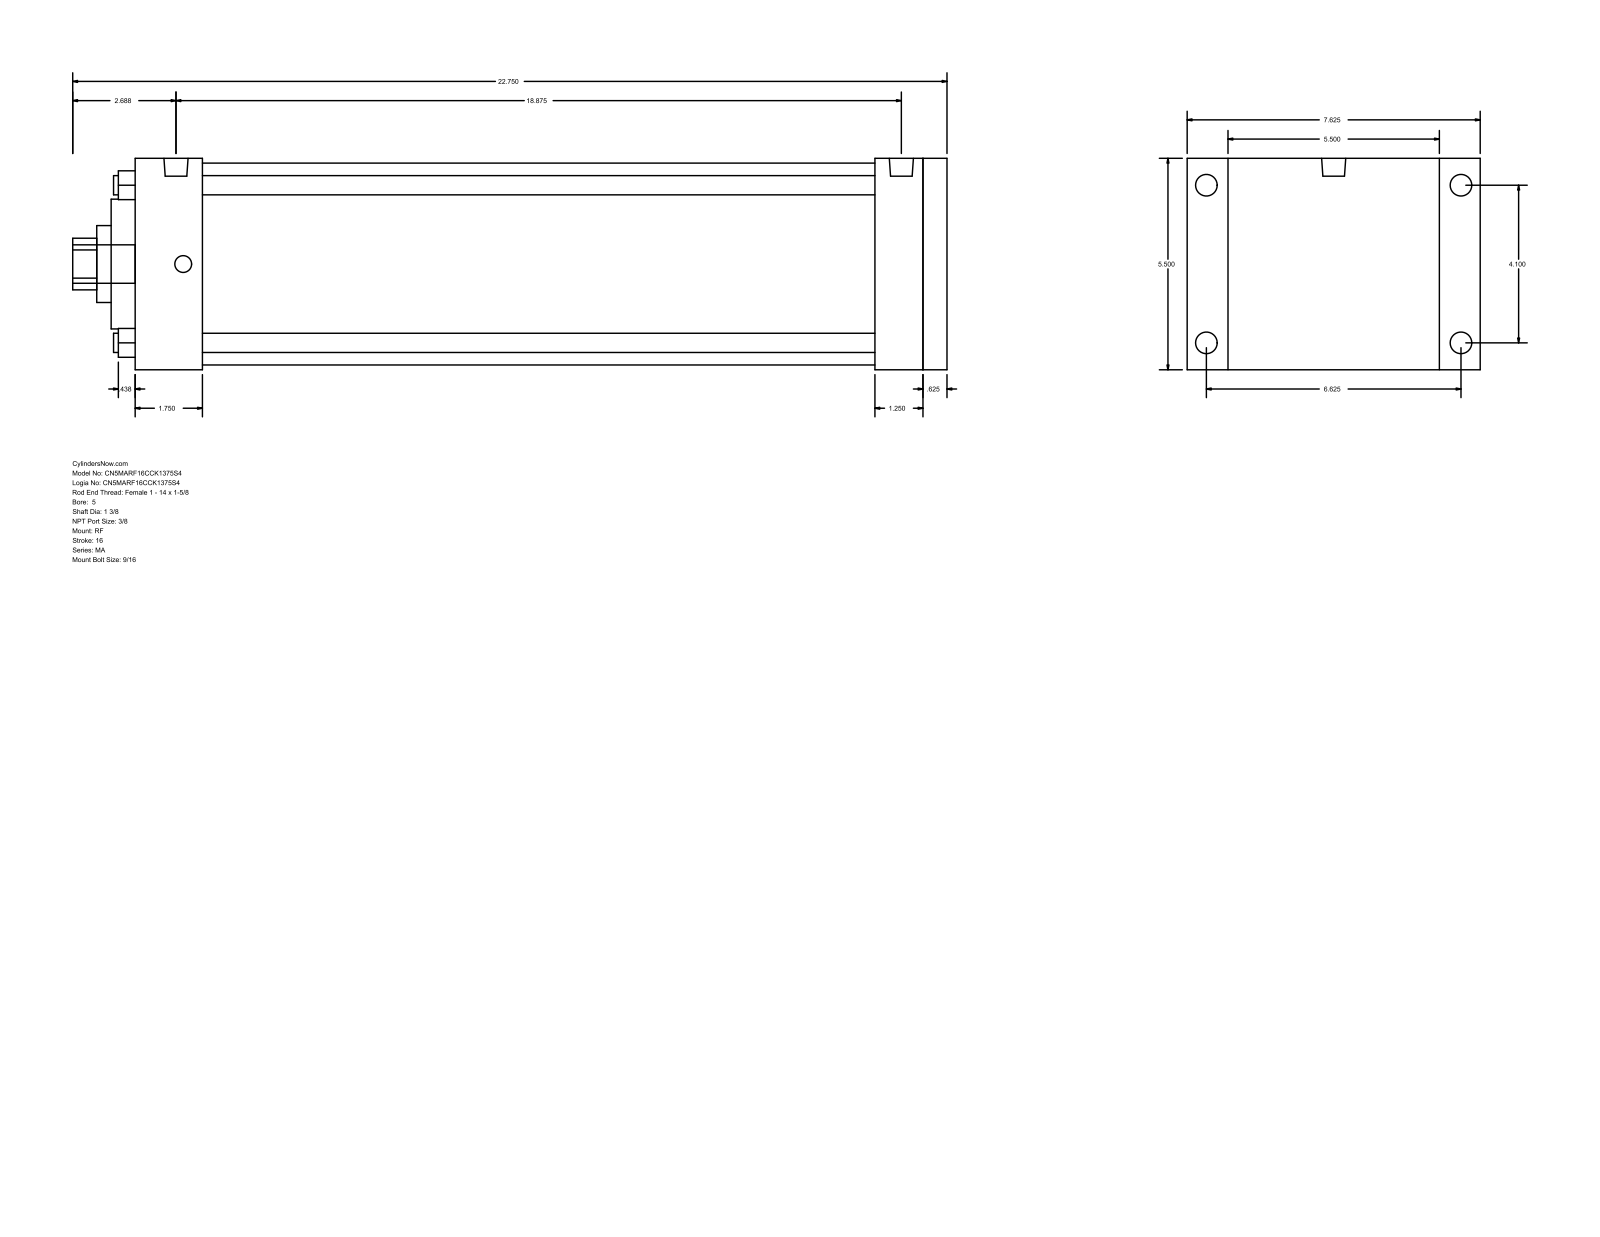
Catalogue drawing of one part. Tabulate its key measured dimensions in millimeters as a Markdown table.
| quantity | value |
| --- | --- |
| part name | MA_RF__0500_1.375 |
| STEP written by | GSSL Pune (CONFIG_CONTROL_DESIGN) |
| units | millimeters |
| bodies | 0 solids, 94 faces (65 planar, 29 cylindrical, 0 other) |
| overall size | 577.85 × 193.68 × 139.7 |
| round holes (diameter × count) | 12.7 × 4, 34.92 × 1, 50.8 × 1, 85.72 × 1, 133.35 × 1 |
| round bosses / shafts (diameter × count) | 14.29 × 4, 11.11 × 4, 15.93 × 2, 25.4 × 1 |
| partial cylindrical surfaces (radius × count) | 17.06 × 1 |
| main face-to-face distances | 139.7, 536.58, 15.87, 520.71, 44.45, 476.26, 492.13, 488.96, 444.51, 31.75 |
| hole center spacings | 73.64, 104.14, 147.28 |
